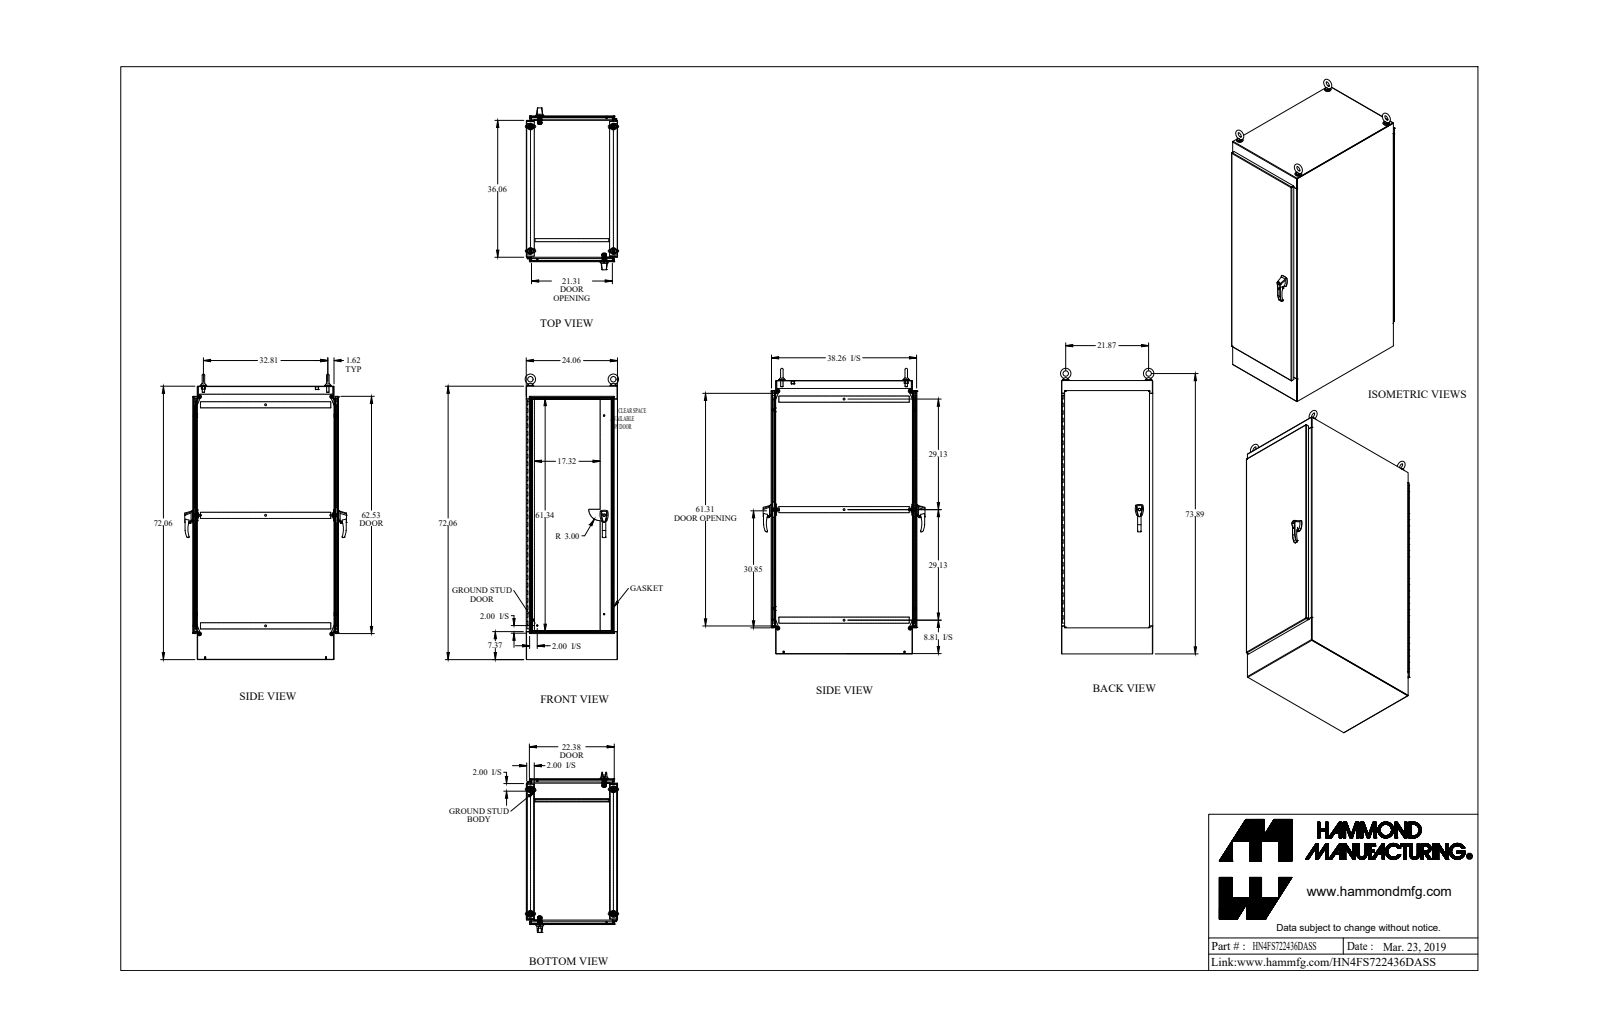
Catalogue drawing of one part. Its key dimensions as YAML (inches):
part_name: "HN4FS722436DASS"
step_written_by: "SolidWorks 2018 (AUTOMOTIVE_DESIGN)"
units: inches
bodies: {solids: 91, faces: 3303, planar: 1445, cylindrical: 1517, other: 341}
overall_size: [75.256, 42.664, 24.604]
volume: 1302
surface_area: 27252
round_holes:
  - {diameter: 0.304, count: 20}
  - {diameter: 0.35, count: 8}
  - {diameter: 0.25, count: 5}
  - {diameter: 0.257, count: 4}
  - {diameter: 0.28, count: 4}
  - {diameter: 0.281, count: 4}
  - {diameter: 0.313, count: 4}
  - {diameter: 0.39, count: 4}
  - {diameter: 0.413, count: 4}
  - {diameter: 0.625, count: 4}
  - {diameter: 0.68, count: 4}
  - {diameter: 0.75, count: 4}
round_bosses_or_shafts:
  - {diameter: 1.75, count: 4}
  - {diameter: 1.5, count: 4}
  - {diameter: 1.25, count: 4}
  - {diameter: 1, count: 4}
  - {diameter: 0.75, count: 4}
  - {diameter: 0.738, count: 4}
  - {diameter: 0.63, count: 4}
  - {diameter: 0.44, count: 4}
partial_cylinders:
  - {radius: 0.125, count: 44}
  - {radius: 0.043, count: 42}
  - {radius: 0.138, count: 36}
  - {radius: 0.017, count: 32}
  - {radius: 0.048, count: 26}
  - {radius: 0.143, count: 26}
  - {radius: 0.5, count: 26}
  - {radius: 0.06, count: 21}
face_to_face_distances: [0.095, 23.965, 23.87, 38.339, 24.06, 71.965, 1.187, 37.152, 38.244, 38.434]
hole_center_spacings: [6, 23.12, 12, 25.349, 18, 28.68, 24, 32.78]
